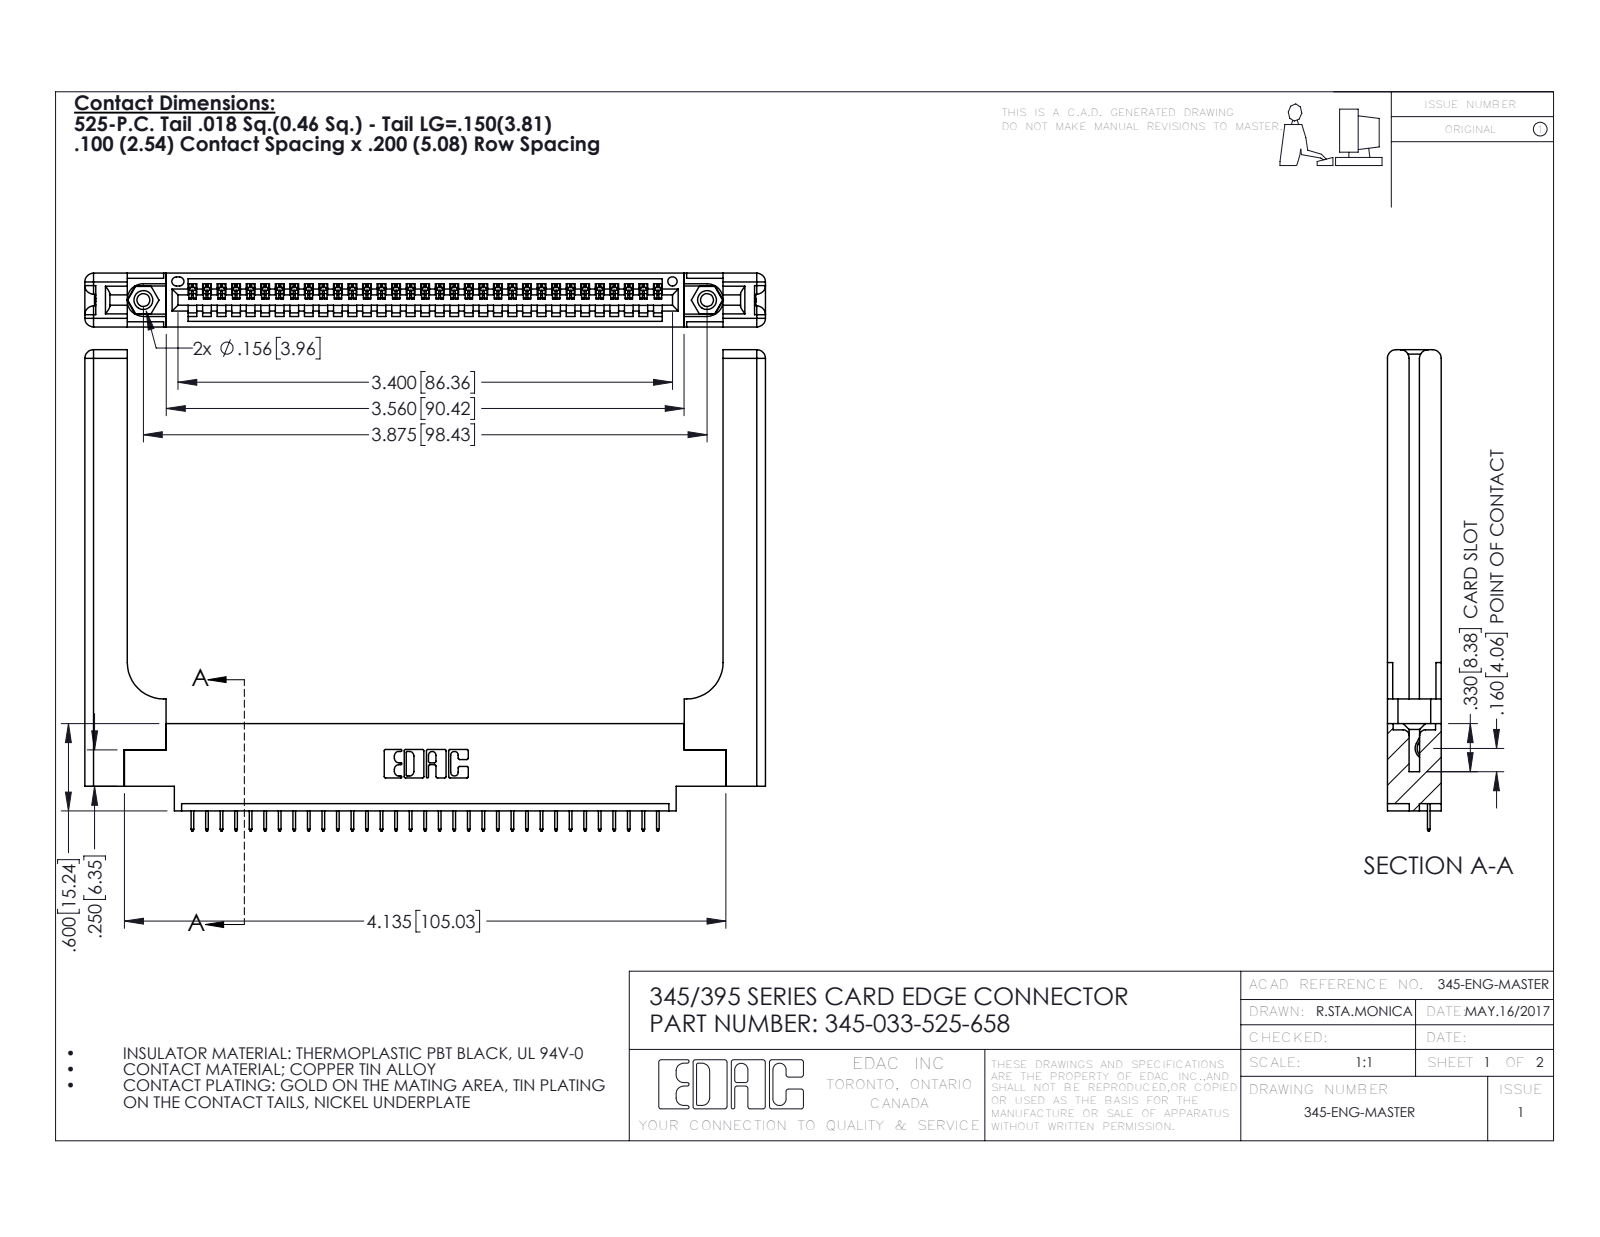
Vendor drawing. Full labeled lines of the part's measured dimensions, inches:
Part name (STEP PRODUCT): 345-220-058_345-220-058; 345-033-525-658; 345-292-001_345-293-125; 345 Part_0.170 Offset - 0.156 Dia-TH (+1 more)
STEP written by: SolidWorks 2020 (CONFIG_CONTROL_DESIGN)
Units: inches
Bodies: 38 solids, 2432 faces (1750 planar, 622 cylindrical, 60 other)
Overall size (bounding box): 4.679 × 3.307 × 0.37
Volume: 1.188 in³ · Surface area: 30.12 in²
Round holes (diameter × count): ⌀0.089 ×2, ⌀0.125 ×2, ⌀0.156 ×2, ⌀0.064 ×1
Round bosses / shafts (diameter × count): ⌀0.155 ×2
Partial cylindrical surfaces — rounded edges, fillets, slot ends (radius × count): R0.006 ×66, R0.01 ×22, R0.06 ×16, R0.007 ×6, R0.031 ×6, R0.026 ×3, R0.03 ×2, R0.031 ×2
Main face-to-face distances: 0.37, 0.072, 0.298, 0.148, 0.15, 0.098, 0.272, 0.025, 0.2, 0.077
Hole centre spacings: 0.27, 3.64, 3.875
